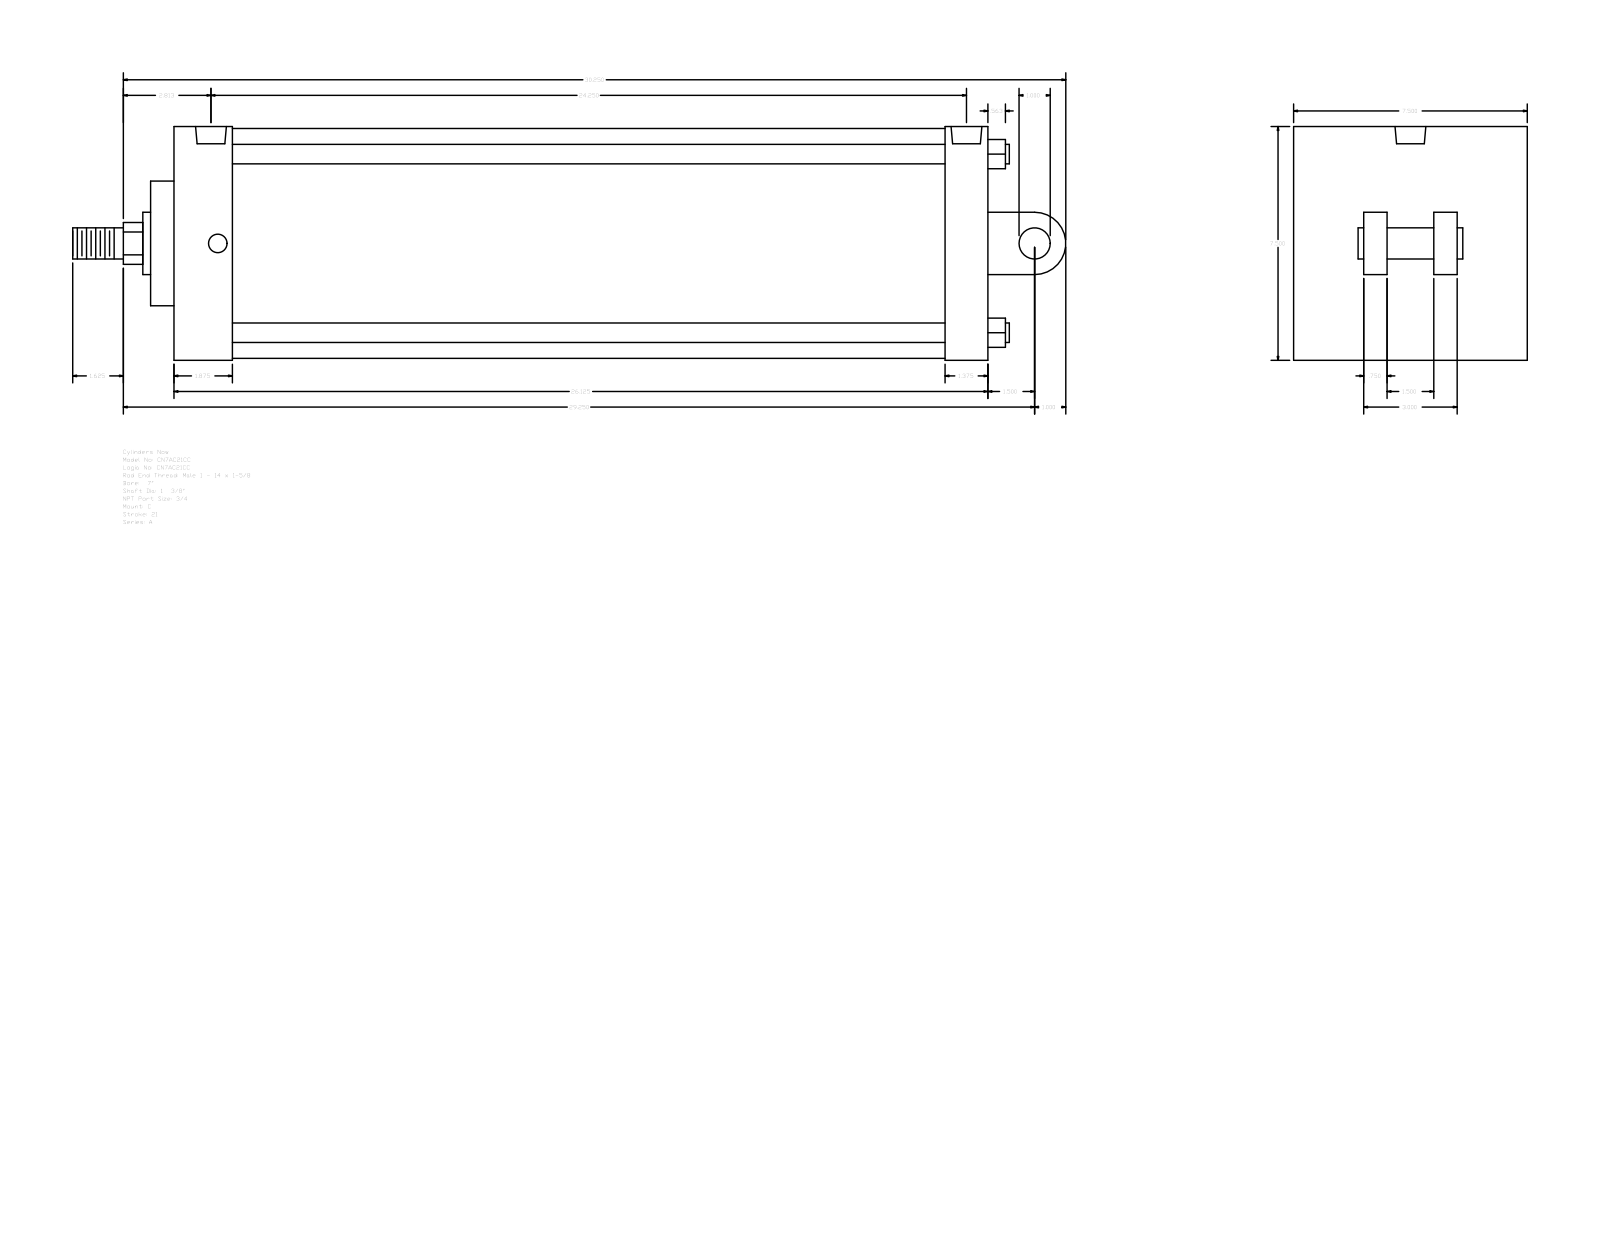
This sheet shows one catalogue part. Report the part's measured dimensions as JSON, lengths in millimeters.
{"part_name": "A_C__0700_1.375", "step_written_by": "GSSL Pune (CONFIG_CONTROL_DESIGN)", "units": "millimeters", "bodies": {"solids": 0, "faces": 104, "planar": 75, "cylindrical": 29, "other": 0}, "overall_size": [809.62, 190.5, 190.5], "round_holes": [[15.08, 4], [25.12, 2]], "round_bosses_or_shafts": [[15.88, 4], [25.4, 2], [187.32, 1], [50.8, 1], [34.92, 1]], "partial_cylinders_radius": [[17.06, 1], [25.4, 1]], "face_to_face_distances": [190.5, 663.58, 76.2, 57.15, 19.04, 682.62, 66.67, 47.63, 615.95, 647.69], "hole_center_spacings": [5.56, 604.83, 610.39, 615.95]}
